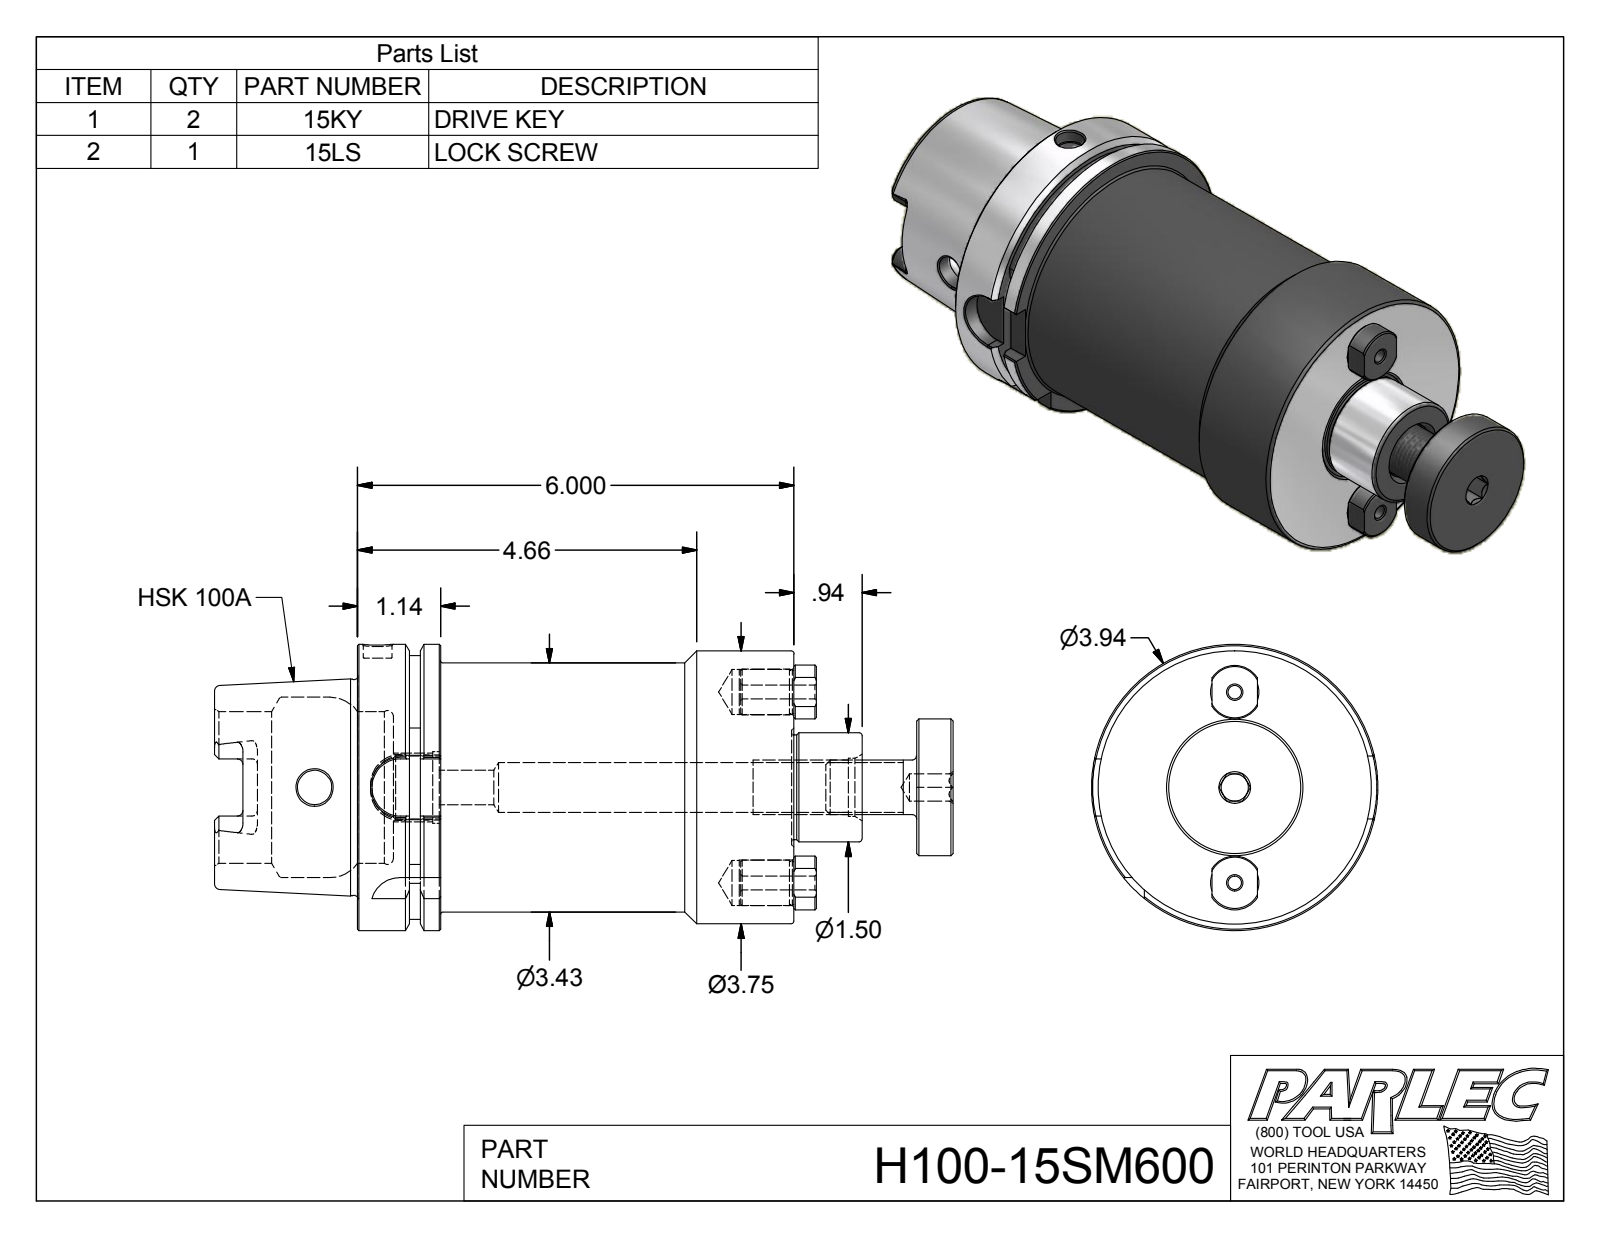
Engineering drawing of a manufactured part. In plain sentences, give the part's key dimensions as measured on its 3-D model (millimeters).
The part is named "H100-15SM600; 15KY; 15LS". Its 3-D file was written by "Autodesk Inventor 2012 (AUTOMOTIVE_DESIGN)". It is 4 solids with 214 faces: 77 planar, 60 cylindrical and 77 other. Overall it measures 258 by 100 by 100 millimeters. Its volume is 1 055 000 cubic millimeters and its surface area 111 000 square millimeters. Round holes: 2 of diameter 4.8, 2 of diameter 12, 2 of diameter 15.7, 2 of diameter 15.8, 1 of diameter 9.5, 1 of diameter 10, 1 of diameter 17.3, 1 of diameter 20.3, 1 of diameter 22.4, 1 of diameter 25, 1 of diameter 53, 1 of diameter 63. Round bosses or shafts: 2 of diameter 15.9, 2 of diameter 15, 1 of diameter 100, 1 of diameter 95.3, 1 of diameter 87, 1 of diameter 75.4, 1 of diameter 47.8, 1 of diameter 38.1. Partial cylindrical surfaces (rounded edges, fillets, slot ends): 6 of radius 2, 4 of radius 4.9, 4 of radius 10, 2 of radius 9.4, 1 of radius 46. The main face-to-face distances are 152.4, 12.5, 207.9, 55.5, 12.7, 139.9, 195.5, 29, 16.5, 123.4. The hole center spacings are 33.3, 66.6.
